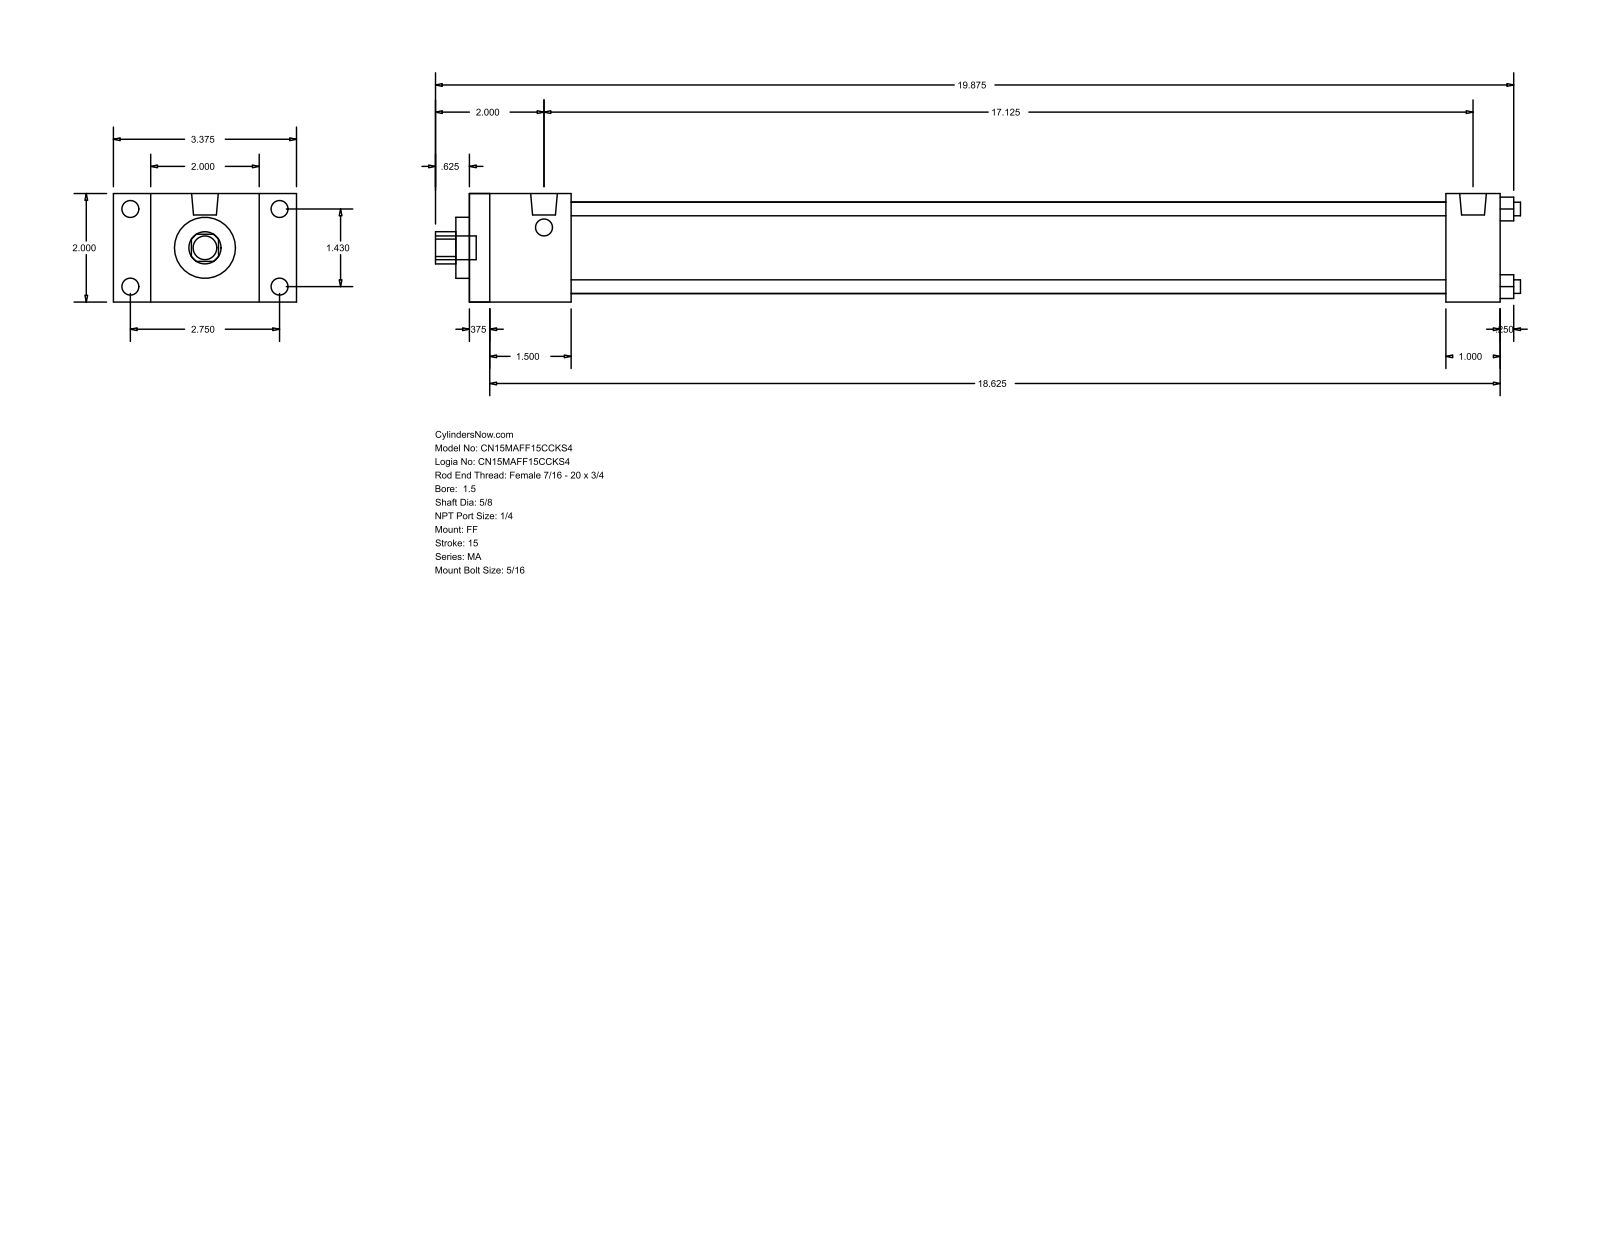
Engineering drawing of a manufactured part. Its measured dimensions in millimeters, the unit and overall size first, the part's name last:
Units: millimetres
Overall size (bounding box): 508 × 85.72 × 50.8
Round holes (diameter × count): ⌀6.35 ×4, ⌀15.88 ×1, ⌀28.57 ×1, ⌀42.93 ×1
Round bosses / shafts (diameter × count): ⌀7.94 ×8, ⌀12.49 ×2, ⌀11.11 ×1
Partial cylindrical surfaces — rounded edges, fillets, slot ends (radius × count): R7.54 ×1
Main face-to-face distances: 50.8, 482.6, 9.52, 473.08, 47.62, 457.19, 38.1, 447.67, 409.57, 434.98
Hole centre spacings: 25.68, 36.32, 51.36
Bodies: 0 solids, 92 faces (64 planar, 28 cylindrical, 0 other)
Part name (STEP PRODUCT): MA_FF__0150_0.625
STEP written by: GSSL Pune (CONFIG_CONTROL_DESIGN)
